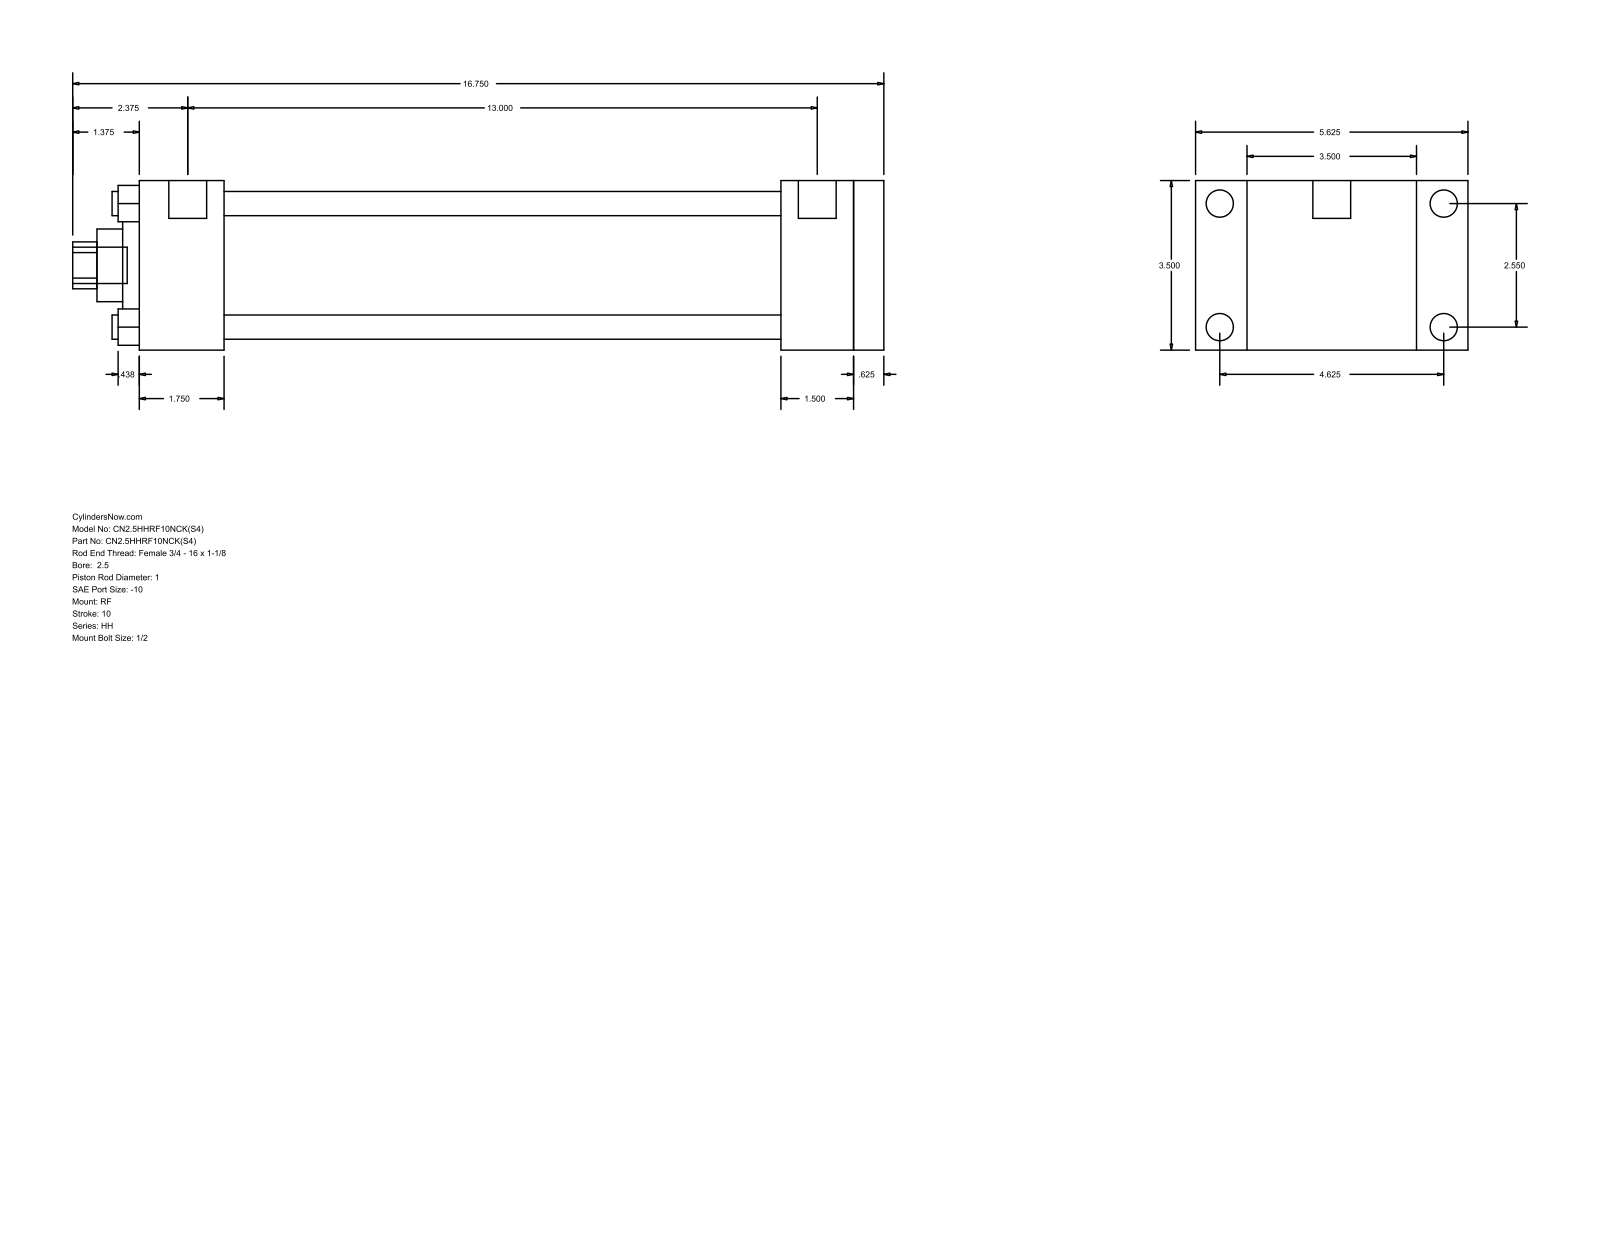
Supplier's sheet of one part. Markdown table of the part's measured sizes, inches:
| quantity | value |
| --- | --- |
| part name | HH_RF__0250_1 |
| STEP written by | GSSL Pune (CONFIG_CONTROL_DESIGN) |
| units | inches |
| bodies | 0 solids, 94 faces (65 planar, 29 cylindrical, 0 other) |
| overall size | 16.75 × 5.625 × 3.5 |
| round holes (diameter × count) | 0.5 × 4, 1 × 1, 1.5 × 1, 2.375 × 1, 2.875 × 1 |
| round bosses / shafts (diameter × count) | 0.563 × 4, 0.219 × 4, 0.781 × 2, 0.75 × 1 |
| partial cylindrical surfaces (radius × count) | 0.484 × 1 |
| main face-to-face distances | 3.5, 0.625, 14.75, 15.375, 1.75, 13, 13.625, 13.25, 11.5, 1.5 |
| hole center spacings | 1.803, 2.55, 3.606 |
